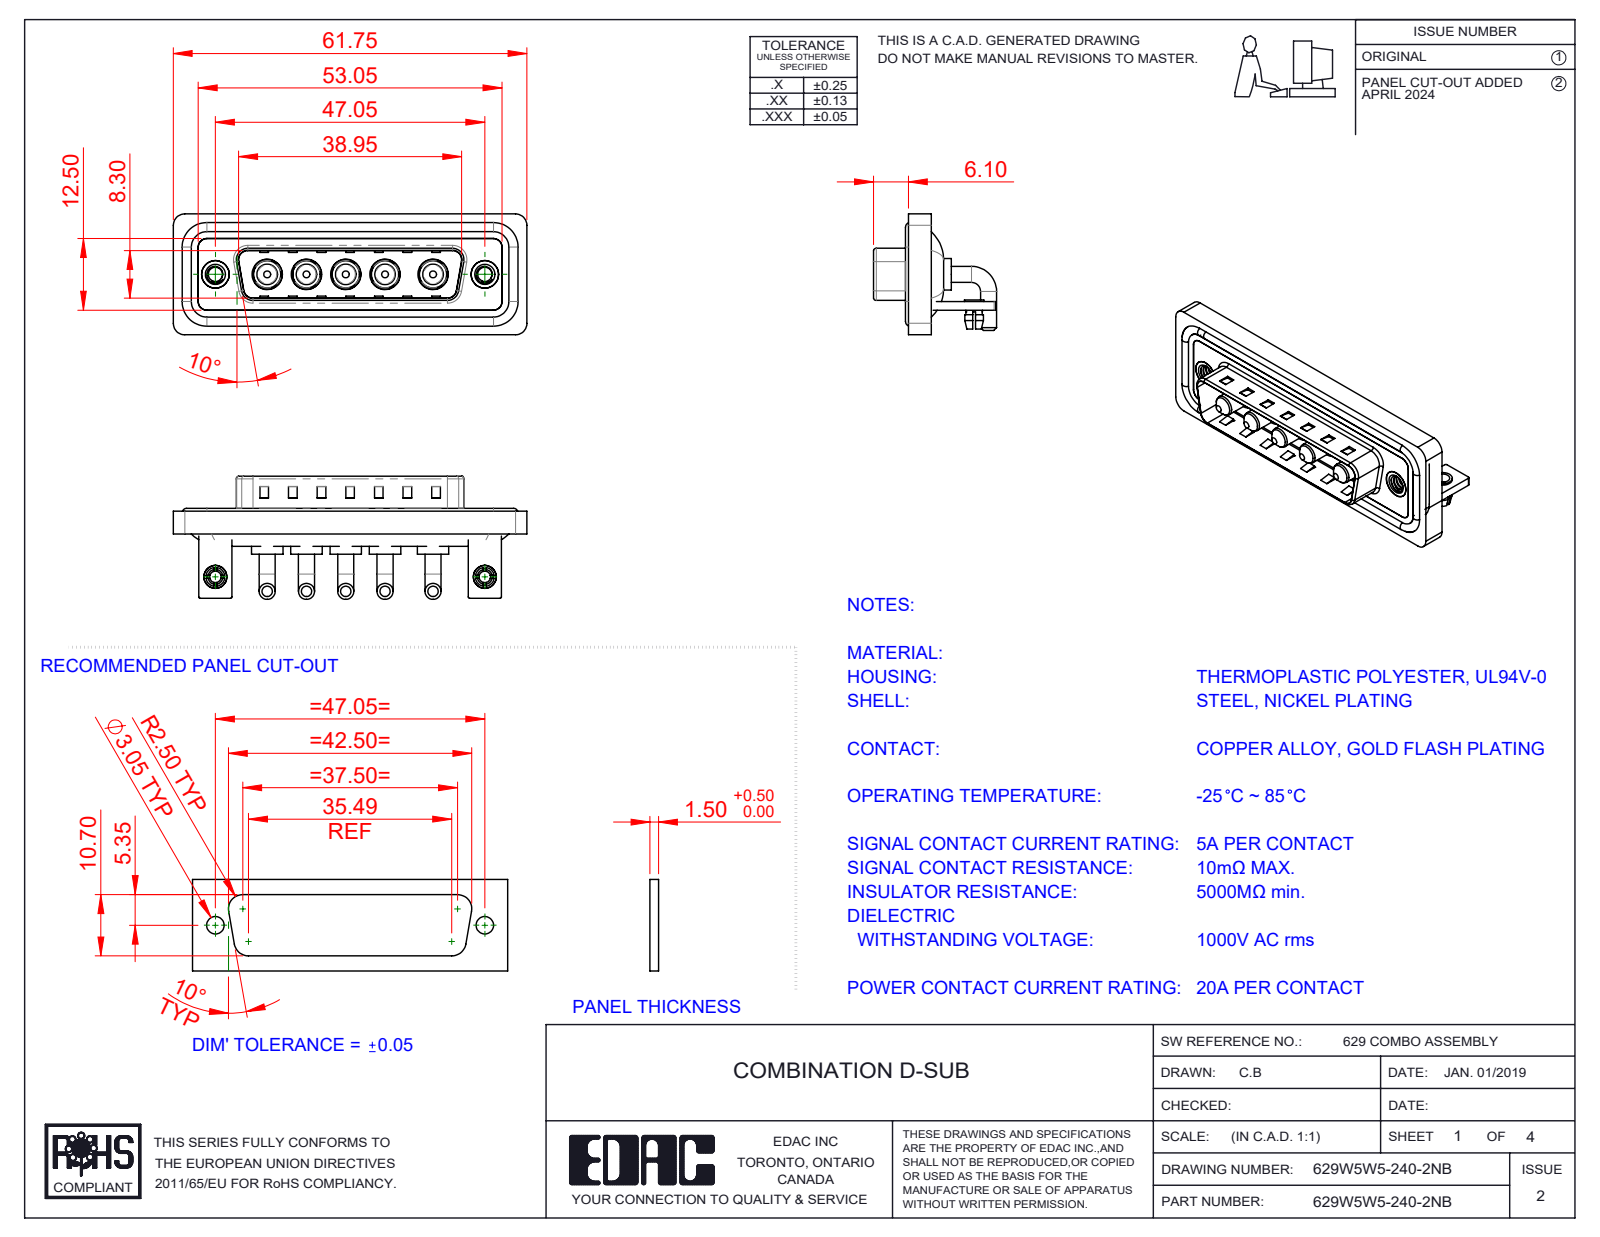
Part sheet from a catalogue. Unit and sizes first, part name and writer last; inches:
Units: inches
Overall size (bounding box): 2.431 × 0.846 × 0.831
Round holes (diameter × count): ⌀0.191 ×5, ⌀0.209 ×5, ⌀0.098 ×4, ⌀0.079 ×2, ⌀0.126 ×2, ⌀0.157 ×2, ⌀0.189 ×2, ⌀0.197 ×2
Round bosses / shafts (diameter × count): ⌀0.11 ×10, ⌀0.217 ×5, ⌀0.205 ×5, ⌀0.187 ×5, ⌀0.148 ×5, ⌀0.142 ×5, ⌀0.063 ×4, ⌀0.193 ×2
Partial cylindrical surfaces — rounded edges, fillets, slot ends (radius × count): R0.079 ×19, R0.059 ×18, R0.01 ×16, R0.02 ×9, R0.063 ×8, R0.083 ×5, R0.024 ×4, R0.026 ×4
Main face-to-face distances: 0.016, 0.059, 0.114, 0.031, 0.083, 0.146, 0.043, 0.177, 0.161, 0.047
Hole centre spacings: 0.27, 0.541, 1.852, 0.27, 0.27, 0.33, 0.33, 0.356
Volume: 0.495 in³ · Surface area: 20.26 in²
Bodies: 21 solids, 828 faces (327 planar, 343 cylindrical, 158 other)
Part name (STEP PRODUCT): Power Pin_20A RA; 629Combo Stabilizer Bracket; 629Combo Threaded Rivet_B; 629Combo Housing_5W5 (+5 more)
STEP written by: SolidWorks 2023 (CONFIG_CONTROL_DESIGN)
